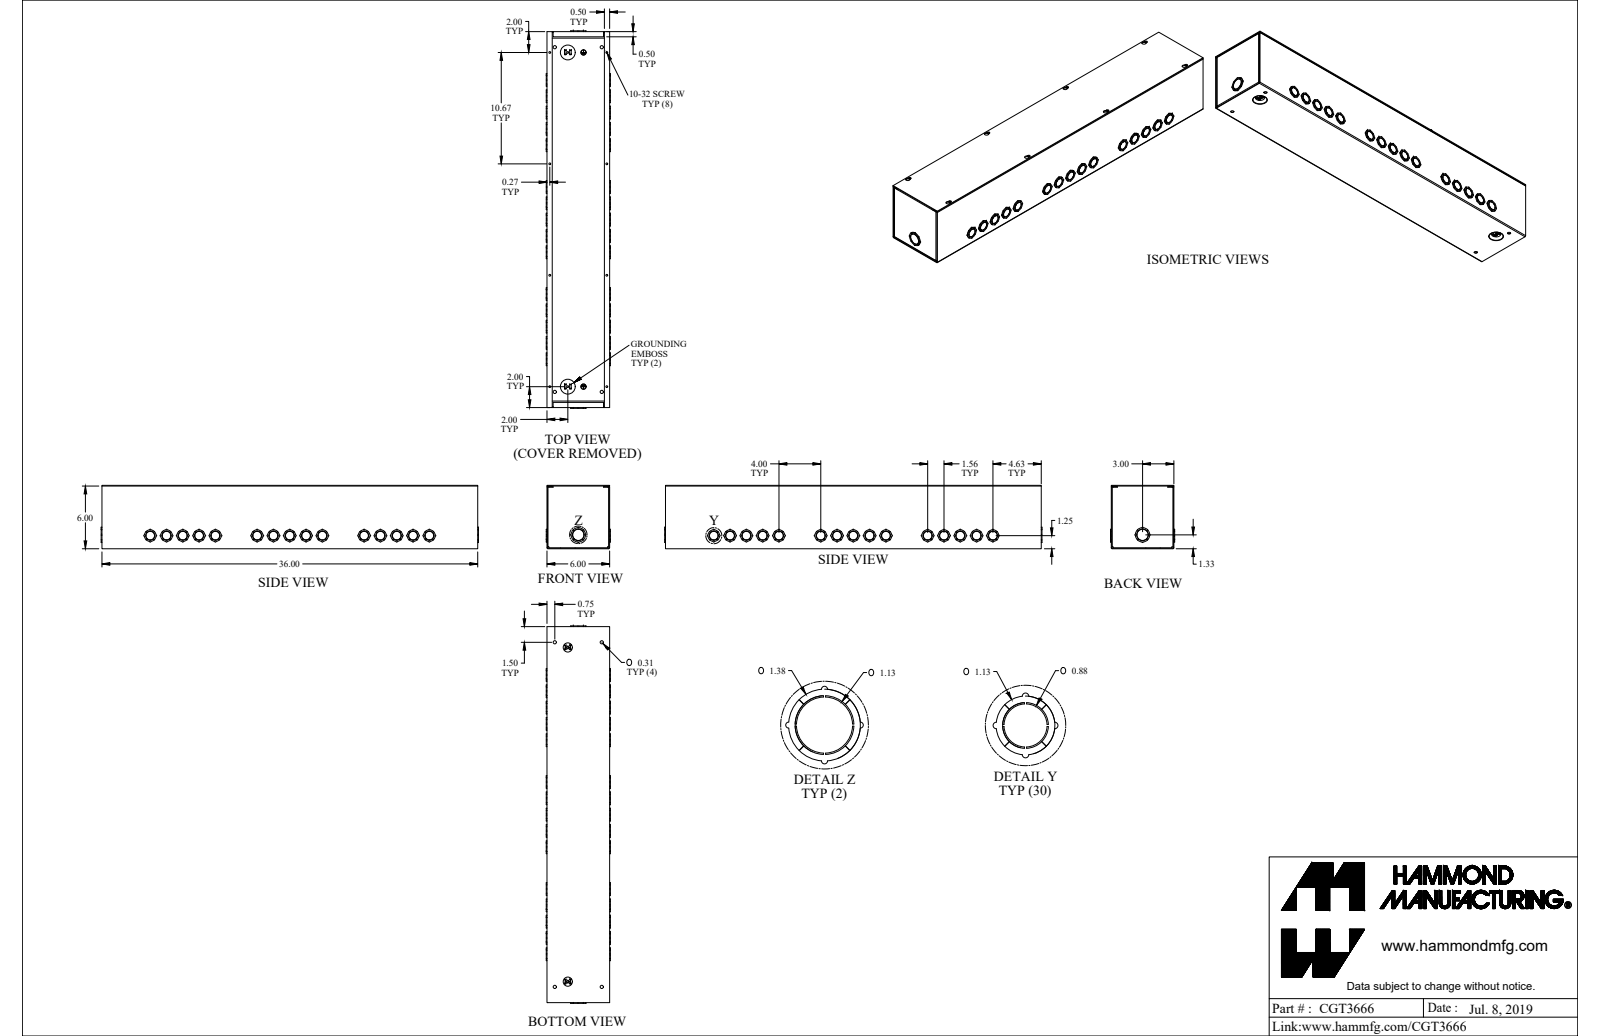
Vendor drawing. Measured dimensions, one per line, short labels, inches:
name: CGT3666
written by: SolidWorks 2021 (AUTOMOTIVE_DESIGN)
unit: in
bodies: 6 solids, 1618 faces (756 planar, 848 cylindrical, 14 other)
size: 36.144 × 6.247 × 6.144
volume: 62.62 in³; area: 1 998 in²
holes: 15× ⌀0.875, 10× ⌀0.17, 4× ⌀0.312, 2× ⌀0.5, 1× ⌀1.125
bosses: 15× ⌀1.125, 15× ⌀0.825, 2× ⌀0.492, 2× ⌀0.375, 2× ⌀0.284, 2× ⌀0.19, 1× ⌀1.375, 1× ⌀1.075
rounds: 60× R0.062, 8× R0.036, 8× R0.057, 8× R0.108, 8× R0.125, 8× R0.203, 4× R0.029, 4× R0.057
face distances: 0.057, 5.943, 6, 0.072, 5.886, 6.072, 6.015, 35.928, 0.129, 36
hole spacings: 3.124, 10.248, 1.562, 1.562, 7.124, 8.686, 11.81, 0.693
